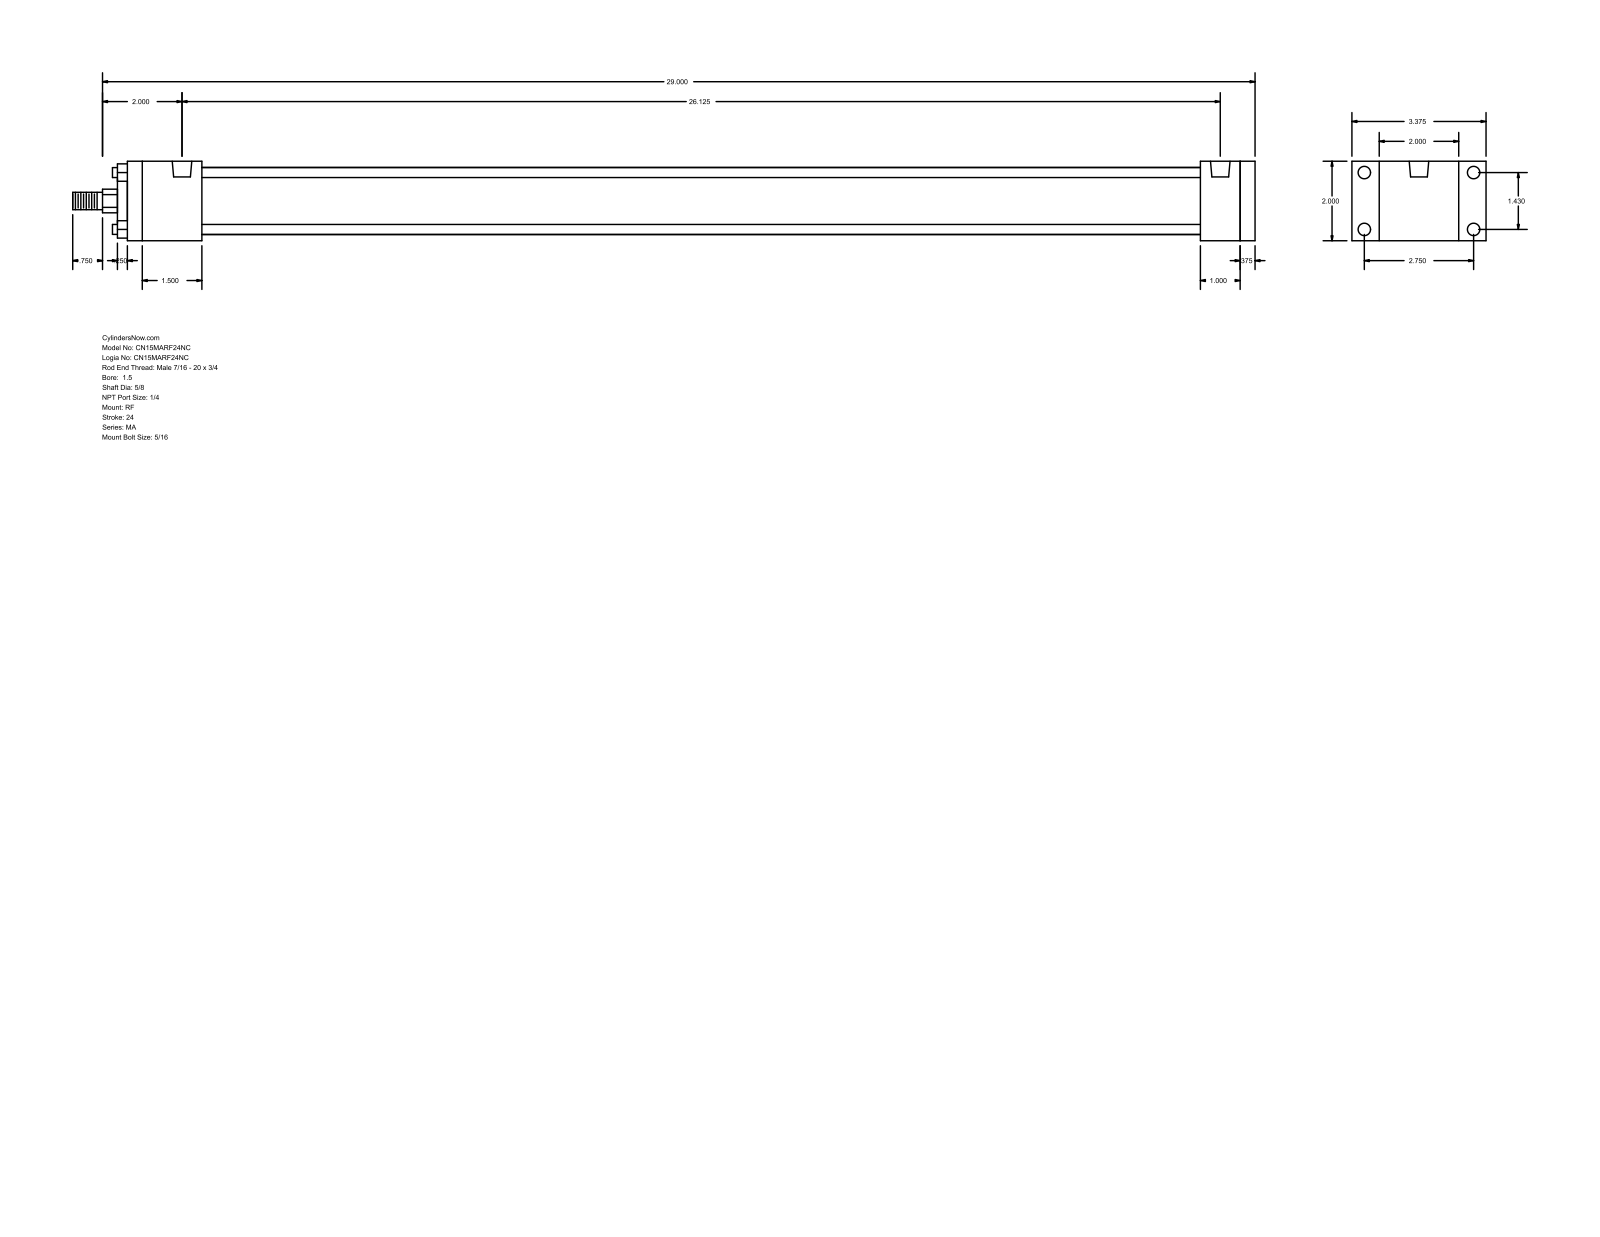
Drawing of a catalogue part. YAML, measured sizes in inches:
part_name: "MA_RF__0150_0.625"
step_written_by: "GSSL Pune (CONFIG_CONTROL_DESIGN)"
units: inches
bodies: {solids: 0, faces: 92, planar: 64, cylindrical: 28, other: 0}
overall_size: [29.75, 3.375, 2]
round_holes:
  - {diameter: 0.313, count: 8}
  - {diameter: 0.492, count: 2}
round_bosses_or_shafts:
  - {diameter: 0.25, count: 4}
  - {diameter: 1.69, count: 1}
  - {diameter: 1.125, count: 1}
  - {diameter: 0.625, count: 1}
  - {diameter: 0.437, count: 1}
partial_cylinders:
  - {radius: 0.297, count: 1}
face_to_face_distances: [2, 28.375, 0.375, 28, 1.375, 27, 1, 1.875, 25.125, 26.125]
hole_center_spacings: [1.43, 2.75, 3.099, 26.125]
